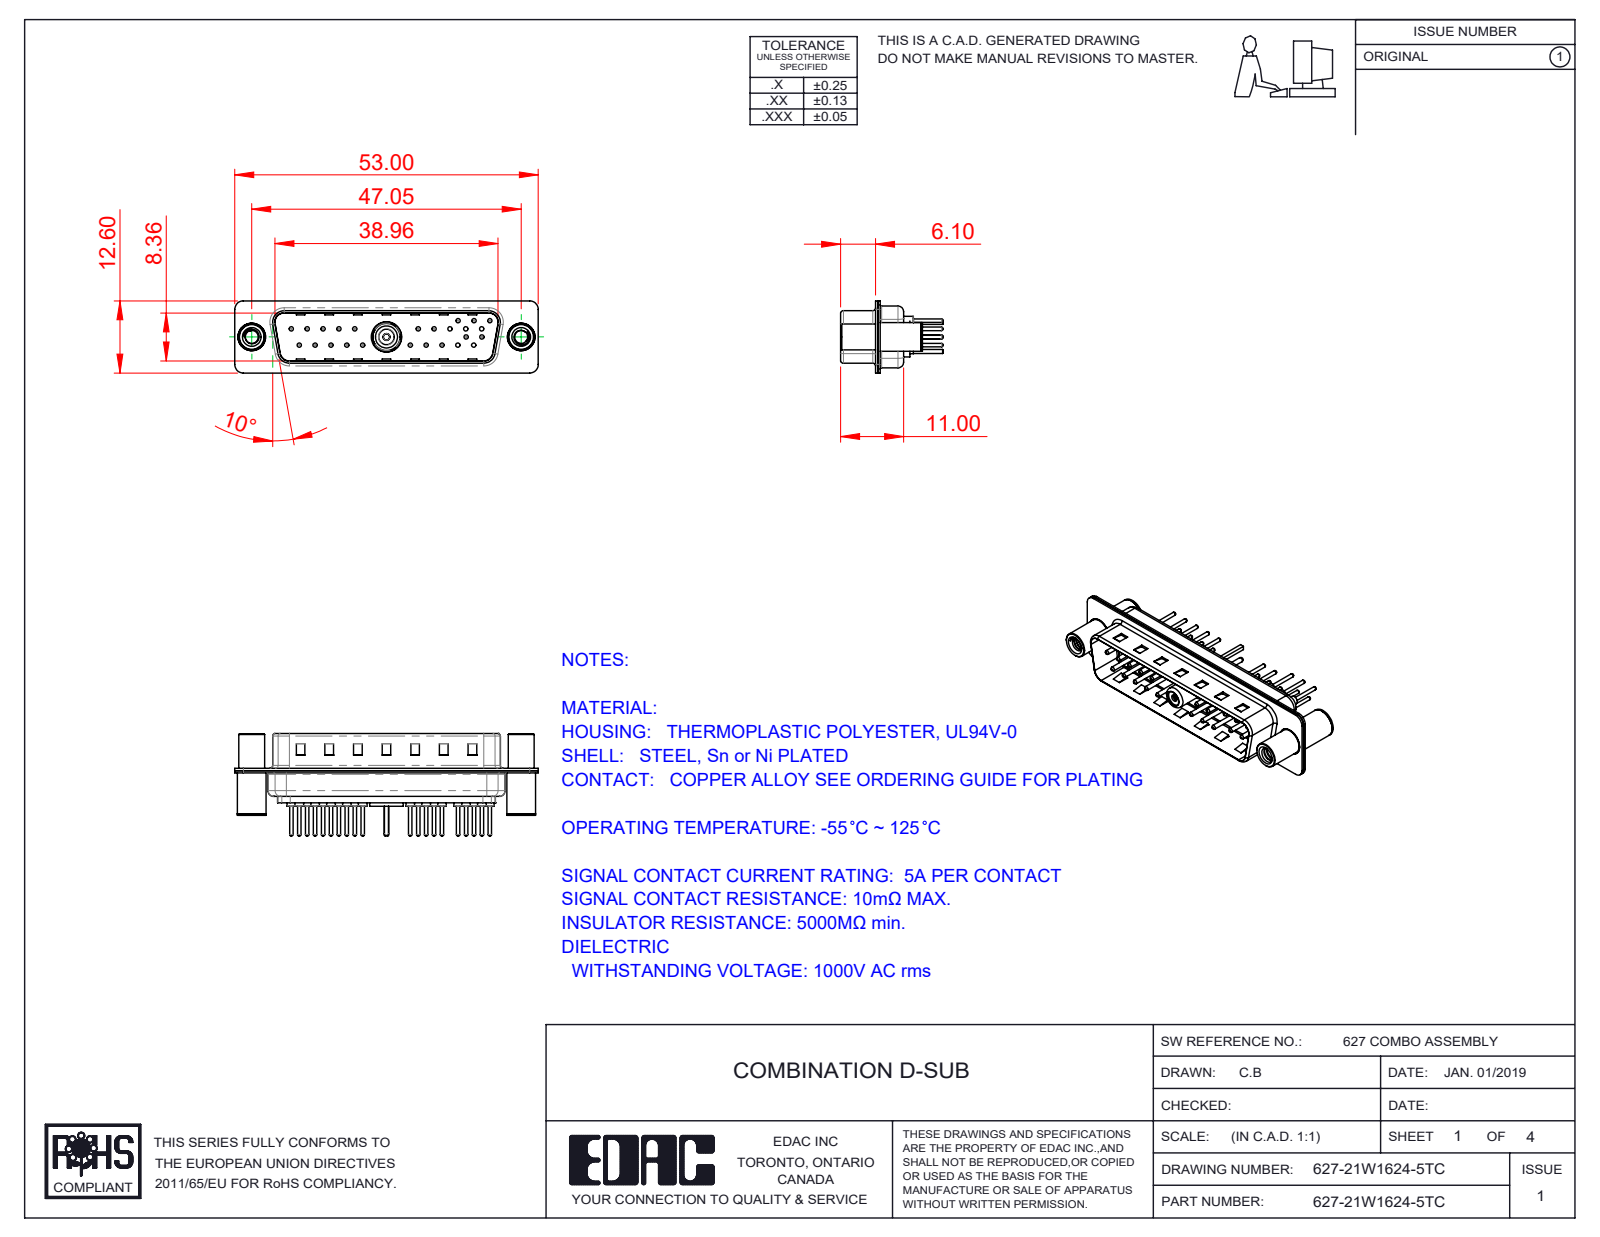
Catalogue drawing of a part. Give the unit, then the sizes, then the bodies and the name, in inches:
Units: inches
Overall size (bounding box): 2.087 × 0.705 × 0.496
Round holes (diameter × count): ⌀0.063 ×21, ⌀0.03 ×20, ⌀0.079 ×20, ⌀0.089 ×2, ⌀0.128 ×2, ⌀0.157 ×2, ⌀0.189 ×2, ⌀0.043 ×1, ⌀0.047 ×1, ⌀0.059 ×1, ⌀0.098 ×1, ⌀0.106 ×1
Round bosses / shafts (diameter × count): ⌀0.059 ×20, ⌀0.024 ×20, ⌀0.079 ×5, ⌀0.03 ×5, ⌀0.197 ×2, ⌀0.193 ×2, ⌀0.177 ×2, ⌀0.23 ×1
Partial cylindrical surfaces — rounded edges, fillets, slot ends (radius × count): R0.059 ×16, R0.079 ×12, R0.02 ×8, R0.063 ×8, R0.01 ×4, R0.024 ×4, R0.026 ×4, R0.035 ×4
Main face-to-face distances: 0.016, 0.032, 0.377, 0.345, 0.059, 0.236, 0.22, 0.048, 0.393, 0.017
Hole centre spacings: 0.124, 0.109, 0.218, 0.327, 0.198, 0.763, 0.826, 0.872
Volume: 0.185 in³ · Surface area: 12.03 in²
Bodies: 30 solids, 1322 faces (364 planar, 526 cylindrical, 432 other)
Part name (STEP PRODUCT): 627Combo Contact Row 2_24; 627Combo Contact Row 1_24; Co-Ax Jack_Straight PC Tail; 627Combo Threaded Standoff and Board Spacer_C (+8 more)
STEP written by: SolidWorks 2016 (CONFIG_CONTROL_DESIGN)
